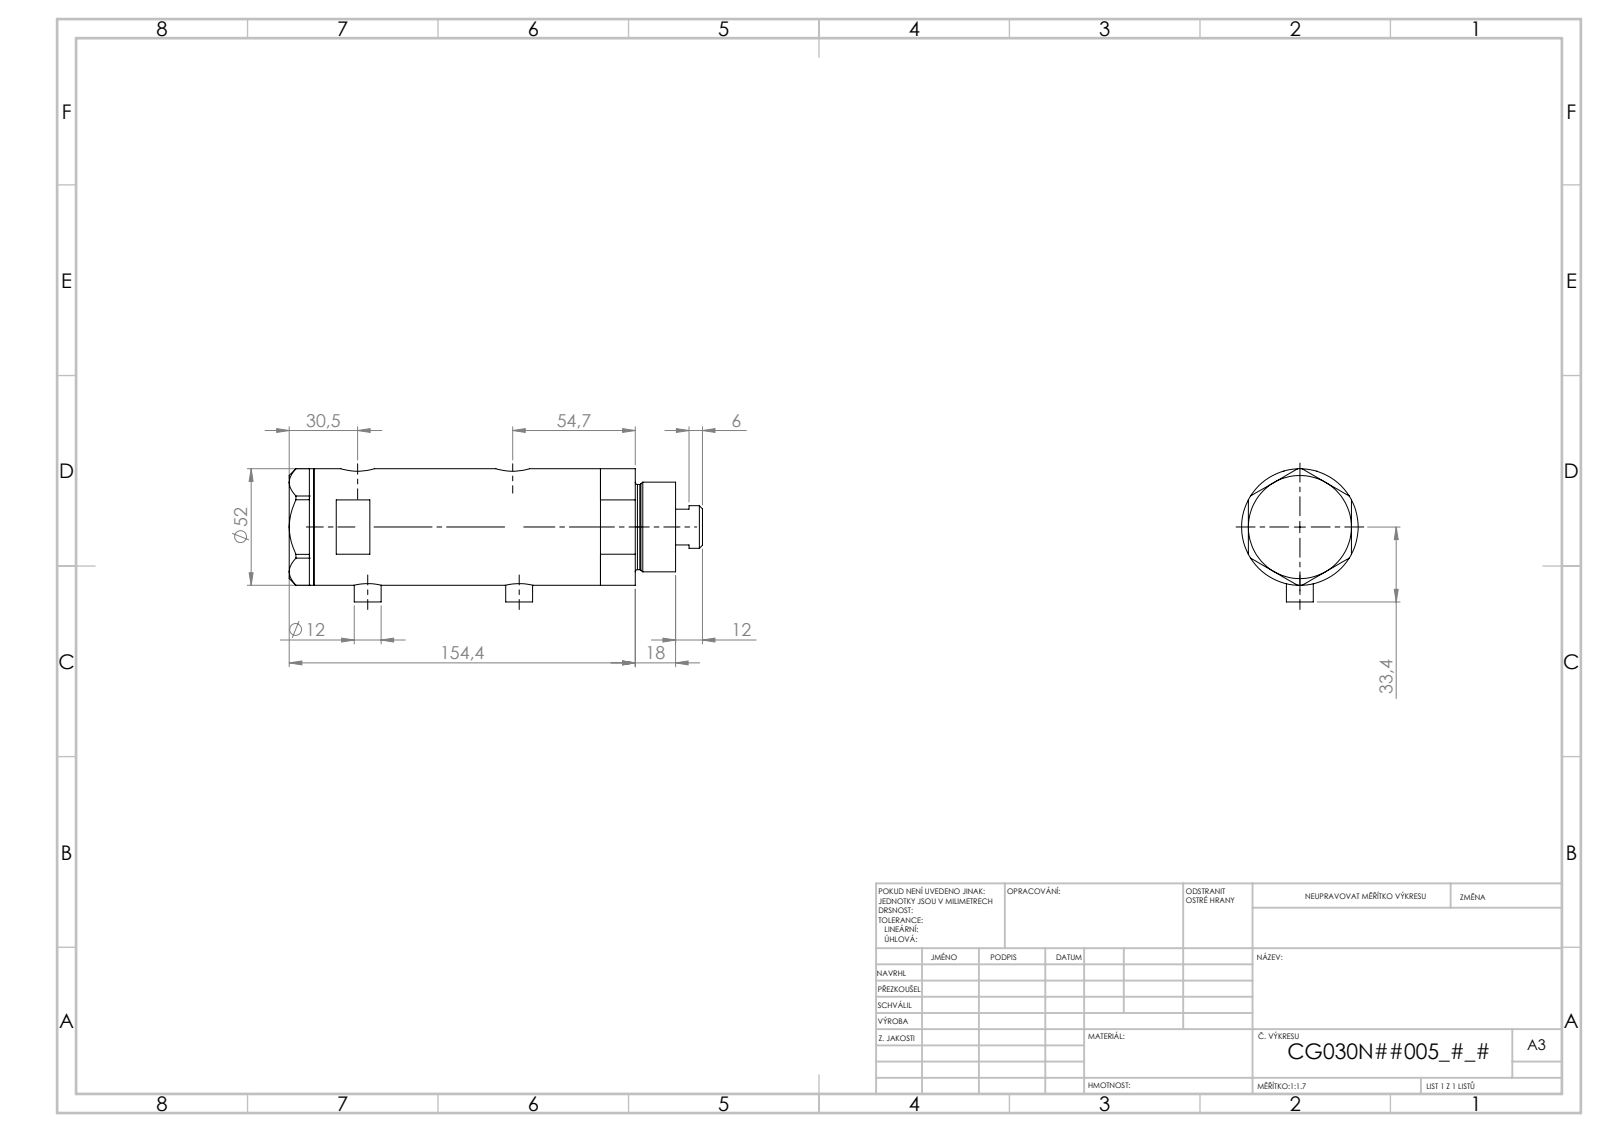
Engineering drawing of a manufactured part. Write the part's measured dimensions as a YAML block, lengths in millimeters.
part_name: "V270CG_VC; V270CG_MIDDLE; V270CG_BACK; V270CG_FRONT"
step_written_by: "SolidWorks 2019 (CONFIG_CONTROL_DESIGN)"
units: millimeters
bodies: {solids: 4, faces: 140, planar: 67, cylindrical: 53, other: 20}
overall_size: [154.02, 53.1, 52]
volume: 276174
surface_area: 66692
round_holes:
  - {diameter: 5, count: 2}
  - {diameter: 9.73, count: 2}
  - {diameter: 12.5, count: 2}
  - {diameter: 15, count: 2}
  - {diameter: 6.5, count: 1}
  - {diameter: 20, count: 1}
  - {diameter: 21.5, count: 1}
  - {diameter: 30, count: 1}
  - {diameter: 33, count: 1}
  - {diameter: 44, count: 1}
round_bosses_or_shafts:
  - {diameter: 12, count: 2}
  - {diameter: 52, count: 1}
  - {diameter: 40, count: 1}
  - {diameter: 38, count: 1}
  - {diameter: 19, count: 1}
face_to_face_distances: [58.56, 23.8, 34.76, 11, 34.8, 69.56, 46, 105.96, 94.96, 71.16]
hole_center_spacings: [2.9, 4.5, 31.75, 34.65, 36.25, 39.15, 2.89, 2.91]
